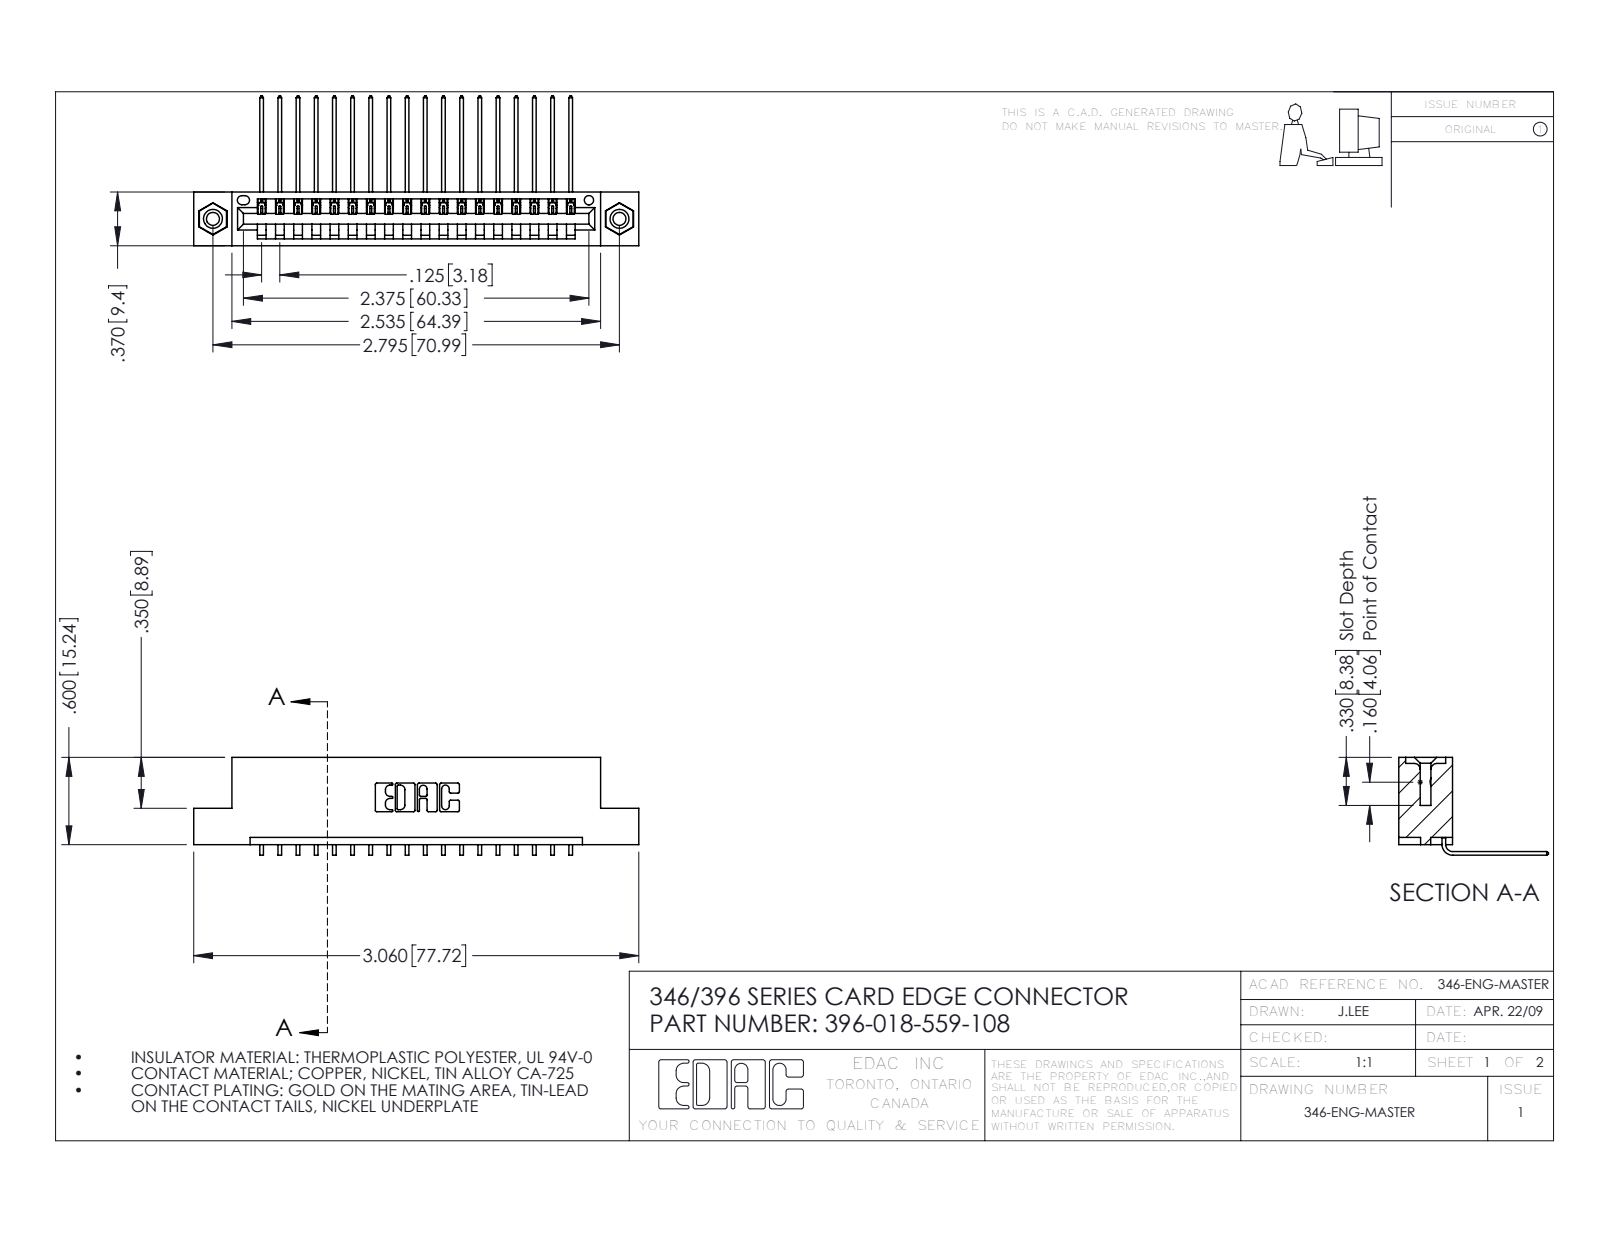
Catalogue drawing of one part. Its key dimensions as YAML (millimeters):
part_name: "345-292-001_558 559 Tail - 1; 346 Part_Flush Mounting Lugs - 0.156 Dia-TI; 396-018-559-108; 345-250-001_345-250-003-102"
step_written_by: "SolidWorks 2016 (CONFIG_CONTROL_DESIGN)"
units: millimeters
bodies: {solids: 21, faces: 1262, planar: 864, cylindrical: 382, other: 16}
overall_size: [77.7, 26.2, 17.1]
volume: 7330
surface_area: 9277
round_holes:
  - {diameter: 2.3, count: 2}
  - {diameter: 3.2, count: 2}
  - {diameter: 4, count: 2}
  - {diameter: 1.6, count: 1}
round_bosses_or_shafts:
  - {diameter: 3.9, count: 2}
partial_cylinders:
  - {radius: 0.2, count: 36}
  - {radius: 0.3, count: 22}
  - {radius: 0.2, count: 6}
  - {radius: 0.8, count: 6}
  - {radius: 0.7, count: 3}
  - {radius: 0.8, count: 2}
  - {radius: 1, count: 2}
  - {radius: 0.4, count: 1}
face_to_face_distances: [1.2, 8.2, 9.4, 6.4, 1.8, 0.6, 7.6, 3.8, 5.6, 2.5]
hole_center_spacings: [6.2, 65.7, 71]
